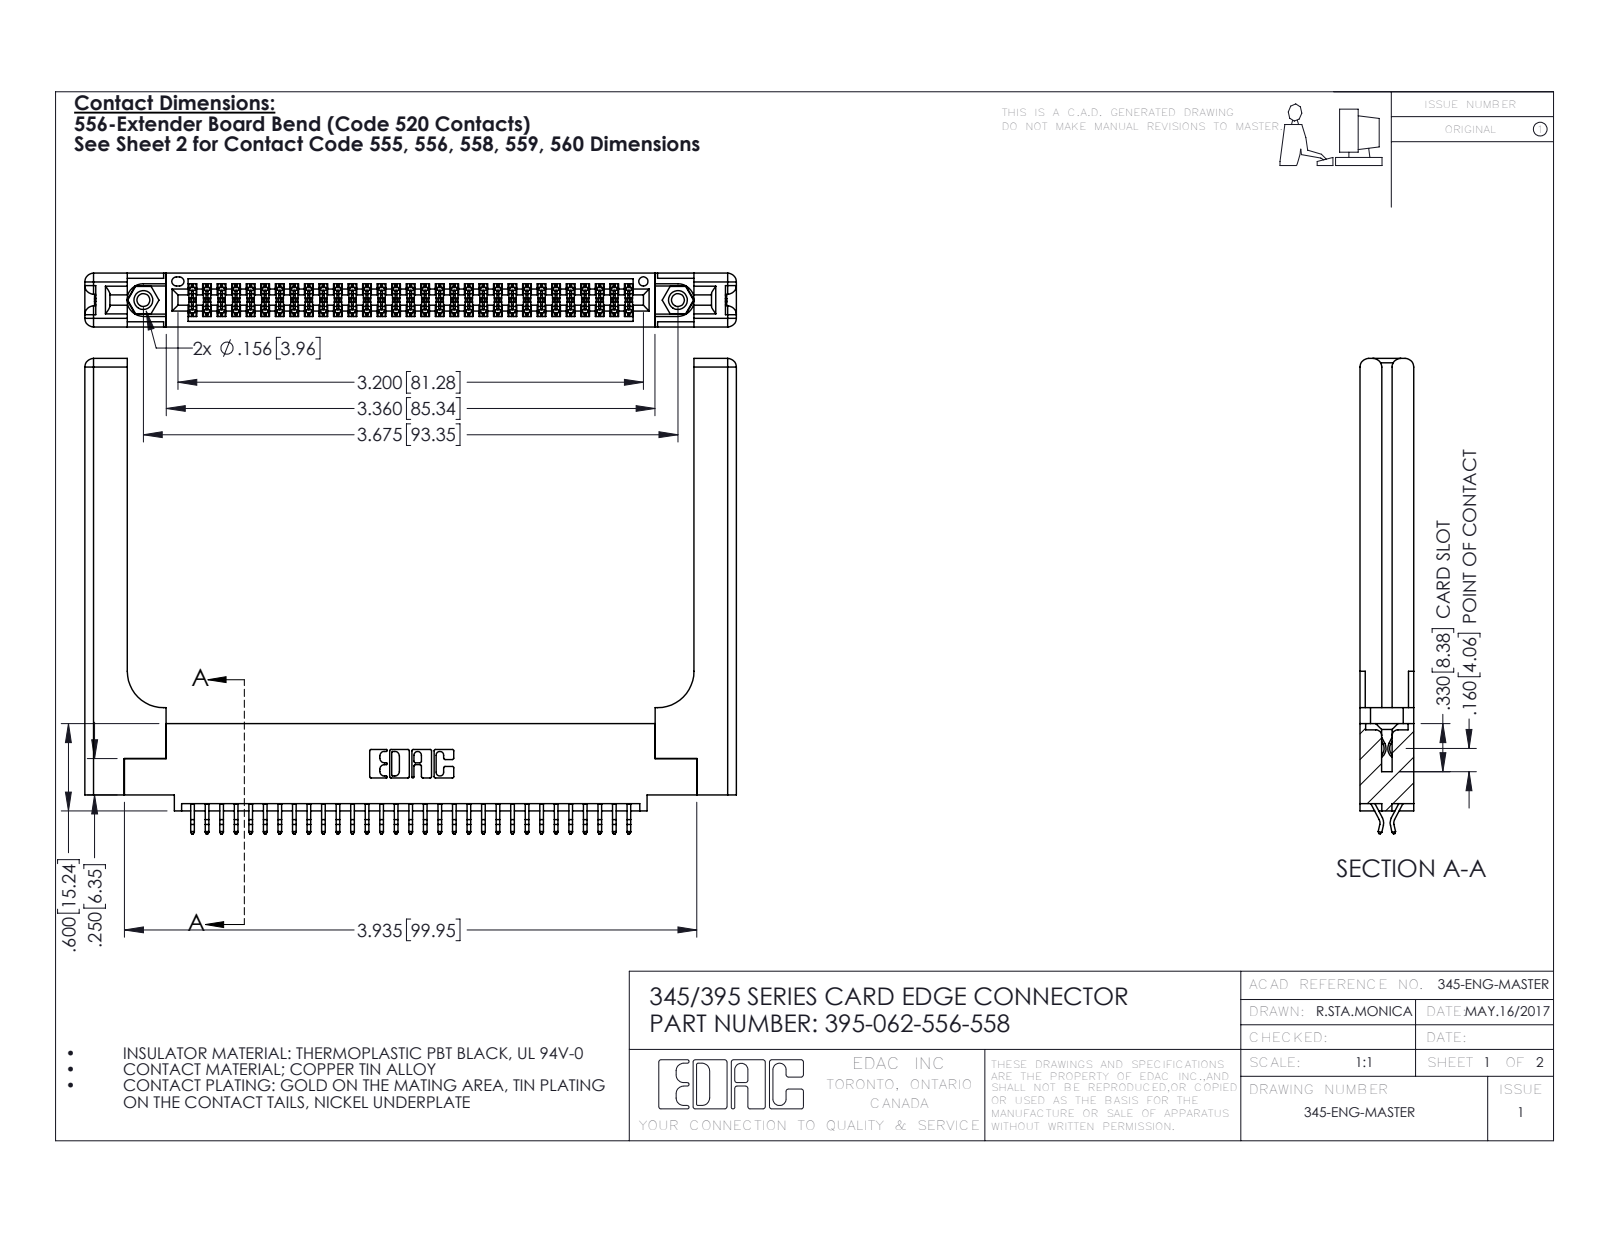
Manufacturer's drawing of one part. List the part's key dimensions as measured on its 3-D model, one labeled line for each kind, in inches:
Part name (STEP PRODUCT): 345-292-001_556 Tail; 345-220-058_345-220-058; 345-250-001_345-250-001-102; 395-062-556-558 (+1 more)
STEP written by: SolidWorks 2016 (CONFIG_CONTROL_DESIGN)
Units: inches
Bodies: 67 solids, 3858 faces (2526 planar, 1272 cylindrical, 60 other)
Overall size (bounding box): 4.479 × 3.267 × 0.37
Volume: 1.181 in³ · Surface area: 32.48 in²
Round holes (diameter × count): ⌀0.089 ×2, ⌀0.125 ×2, ⌀0.156 ×2, ⌀0.064 ×1
Round bosses / shafts (diameter × count): ⌀0.155 ×2
Partial cylindrical surfaces — rounded edges, fillets, slot ends (radius × count): R0.006 ×93, R0.01 ×22, R0.06 ×16, R0.007 ×6, R0.031 ×6, R0.026 ×3, R0.01 ×2, R0.014 ×2
Main face-to-face distances: 0.37, 0.072, 0.298, 0.025, 0.225, 0.098, 0.272, 0.2, 0.148, 0.15
Hole centre spacings: 0.27, 3.44, 3.675
